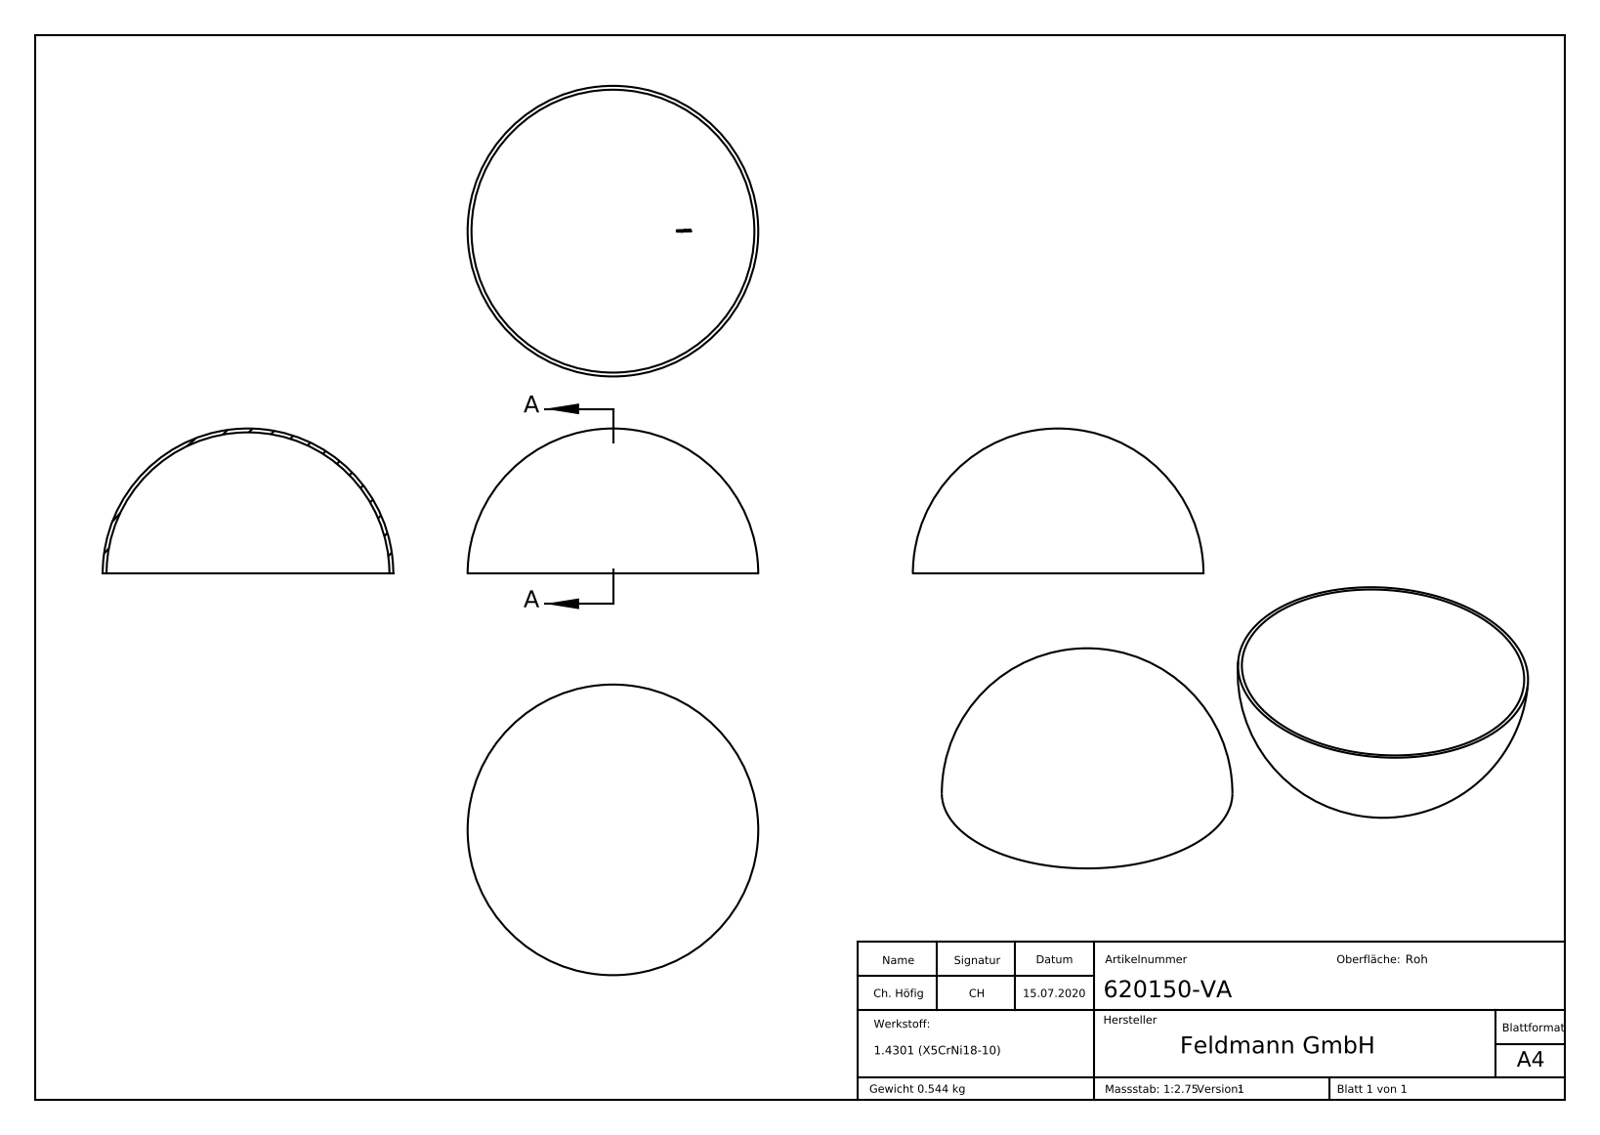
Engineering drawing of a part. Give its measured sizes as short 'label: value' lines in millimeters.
name: 620150-VA
written by: SolidWorks 2018 (CONFIG_CONTROL_DESIGN)
unit: mm
bodies: 1 solid, 213 faces (98 planar, 0 cylindrical, 115 other)
size: 150 × 150 × 75
volume: 68 818 mm³; area: 69 760 mm²
face distances: 0.53, 0.45, 5.1, 3.79, 0.61, 1.19, 0.55, 0.5, 0.81, 1.31
